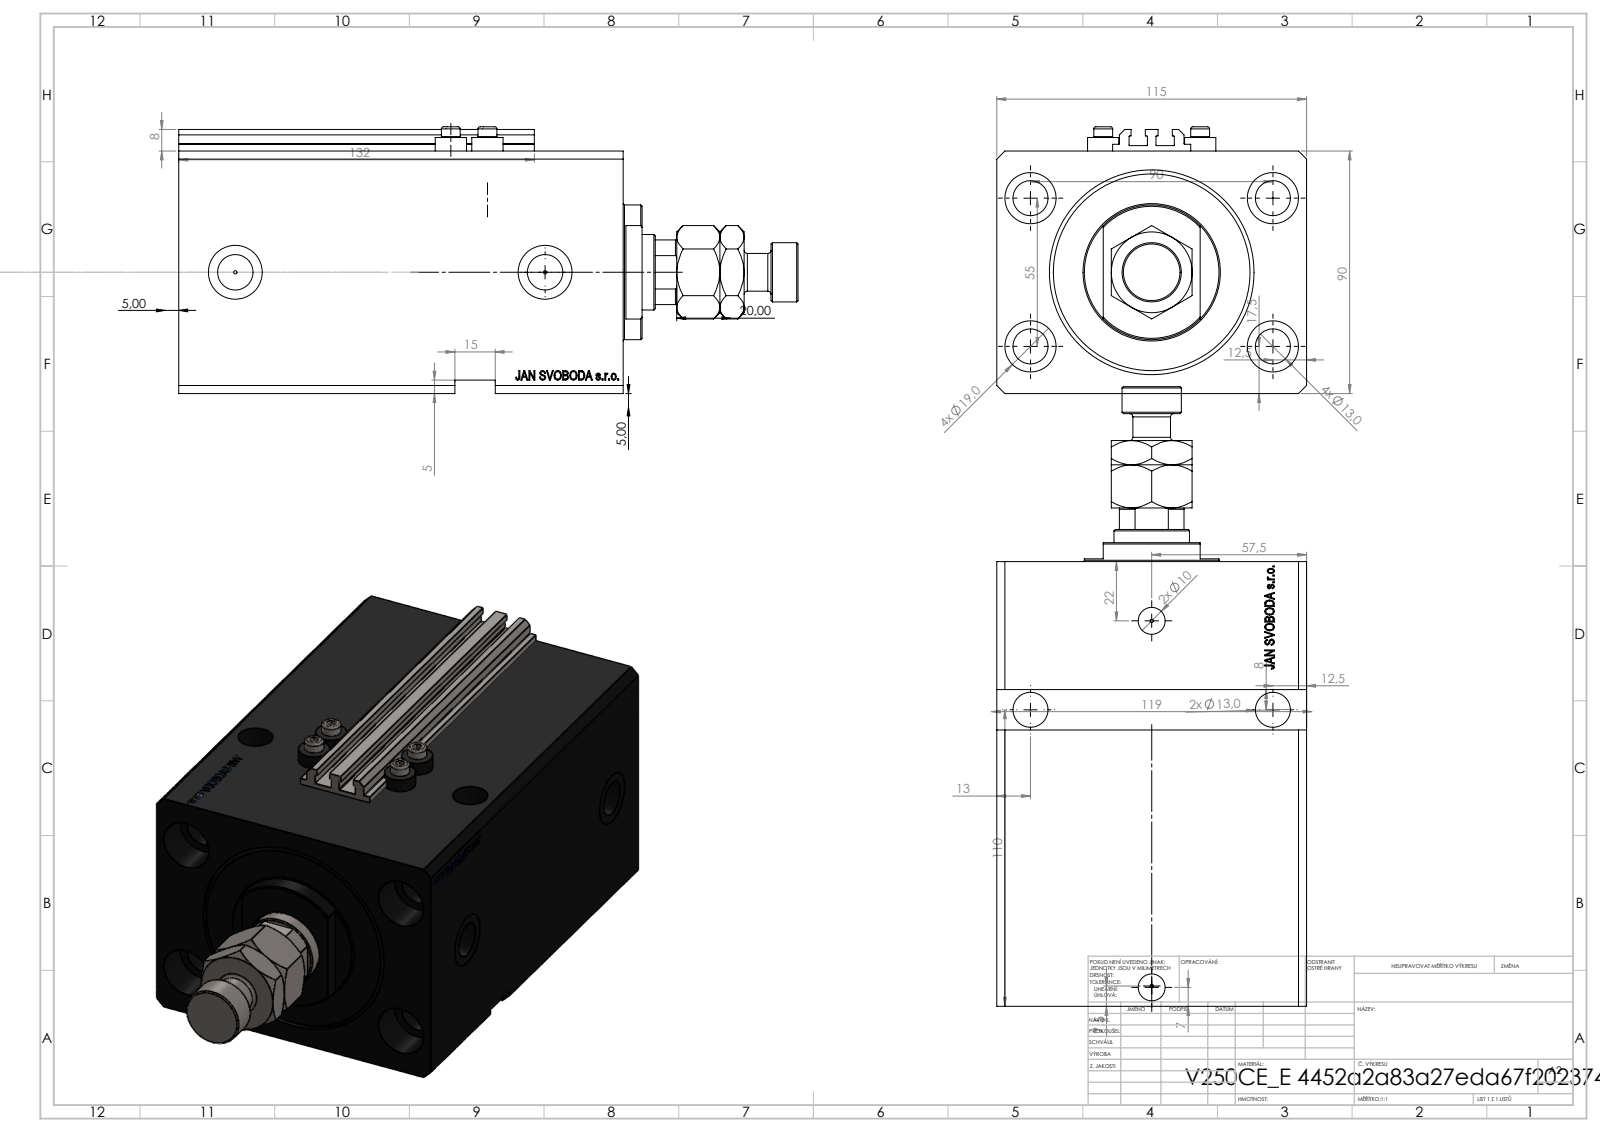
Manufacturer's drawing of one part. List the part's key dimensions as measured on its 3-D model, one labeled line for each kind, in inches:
Part name (STEP PRODUCT): V250CE_E_Body; MFA; ALLEN BOLT V250CE; V250CE_C_VCP (+1 more)
STEP written by: SolidWorks 2019 (CONFIG_CONTROL_DESIGN)
Units: inches
Bodies: 9 solids, 1183 faces (563 planar, 150 cylindrical, 470 other)
Overall size (bounding box): 9.055 × 4.528 × 3.898
Volume: 86.35 in³ · Surface area: 341.2 in²
Round holes (diameter × count): ⌀0.512 ×6, ⌀0.049 ×4, ⌀0.157 ×4, ⌀0.748 ×4, ⌀0.335 ×2, ⌀0.394 ×2, ⌀0.518 ×2, ⌀0.787 ×2, ⌀0.728 ×1, ⌀1.102 ×1, ⌀2.48 ×1, ⌀2.992 ×1
Round bosses / shafts (diameter × count): ⌀0.457 ×4, ⌀0.276 ×4, ⌀1.969 ×1, ⌀0.866 ×1, ⌀0.551 ×1
Partial cylindrical surfaces — rounded edges, fillets, slot ends (radius × count): R0.008 ×10, R0.531 ×1
Main face-to-face distances: 3.543, 4.528, 0.787, 6.496, 0.705, 5.791, 5.709, 5.004, 2.559, 0.512
Hole centre spacings: 2.076, 3.543, 0.535, 0.581, 1.078, 1.083, 1.12, 1.17
